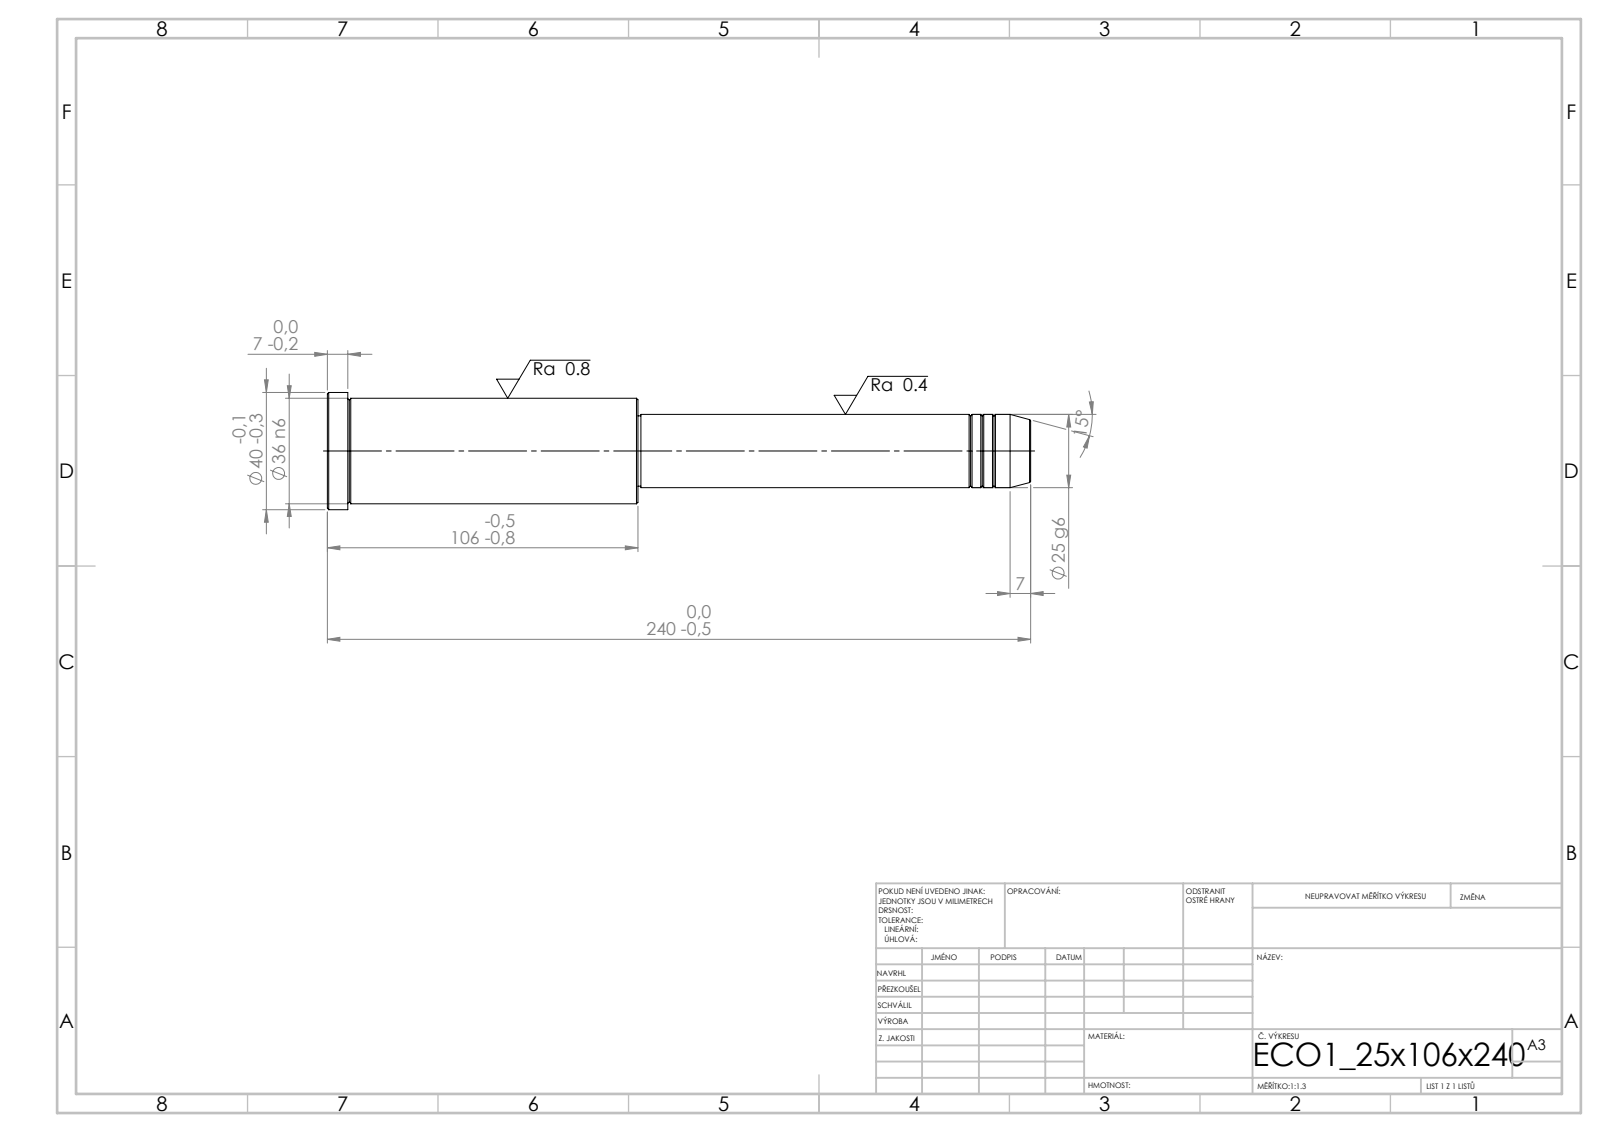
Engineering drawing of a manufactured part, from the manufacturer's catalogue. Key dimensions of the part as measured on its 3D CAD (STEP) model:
STEP written by: SolidWorks 2019 (CONFIG_CONTROL_DESIGN)
Units: millimetres
Bodies: 1 solid, 43 faces (5 planar, 14 cylindrical, 24 other)
Overall size (bounding box): 240 × 40 × 40
Volume: 174 649 mm³ · Surface area: 25 136 mm²
Round bosses / shafts (diameter × count): ⌀40 ×1, ⌀36 ×1, ⌀25 ×1, ⌀24 ×1
Main face-to-face distances: 106, 134, 240, 233, 99, 7, 133, 1, 100, 107
